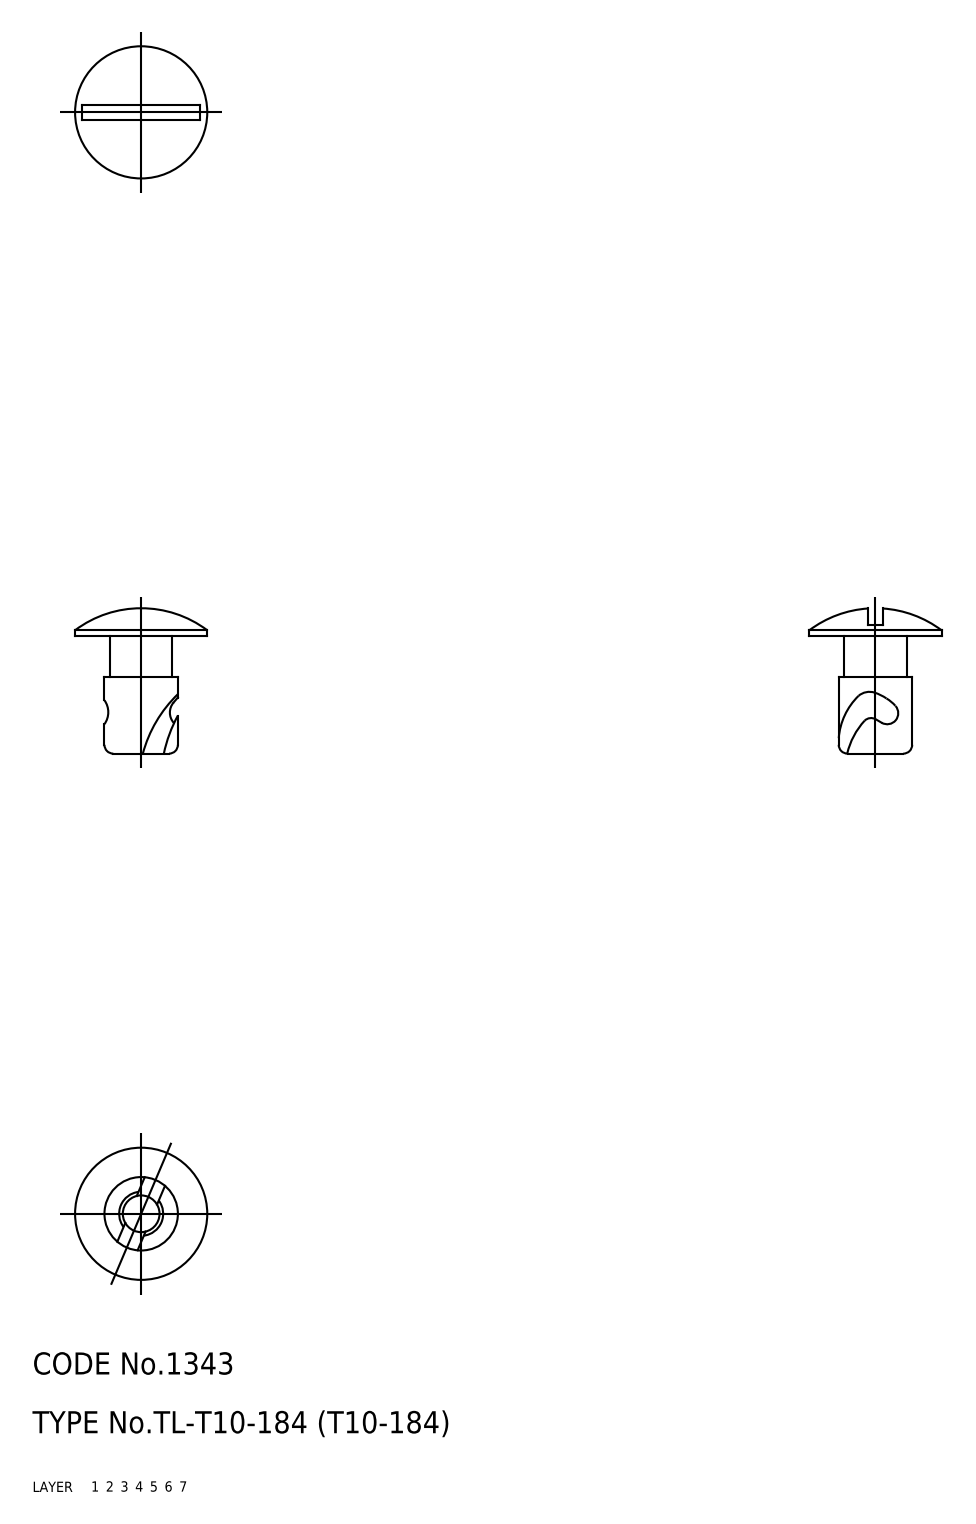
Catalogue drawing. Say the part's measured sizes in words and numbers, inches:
The part is named "fastener". Its 3-D file was written by "CADfix (AUTOMOTIVE_DESIGN)". It is 1 solid with 36 faces: 0 planar, 0 cylindrical and 36 other. Overall it measures 0.778 by 0.709 by 0.709 inches. Its volume is 0.082 cubic inches and its surface area 1.961 square inches.
